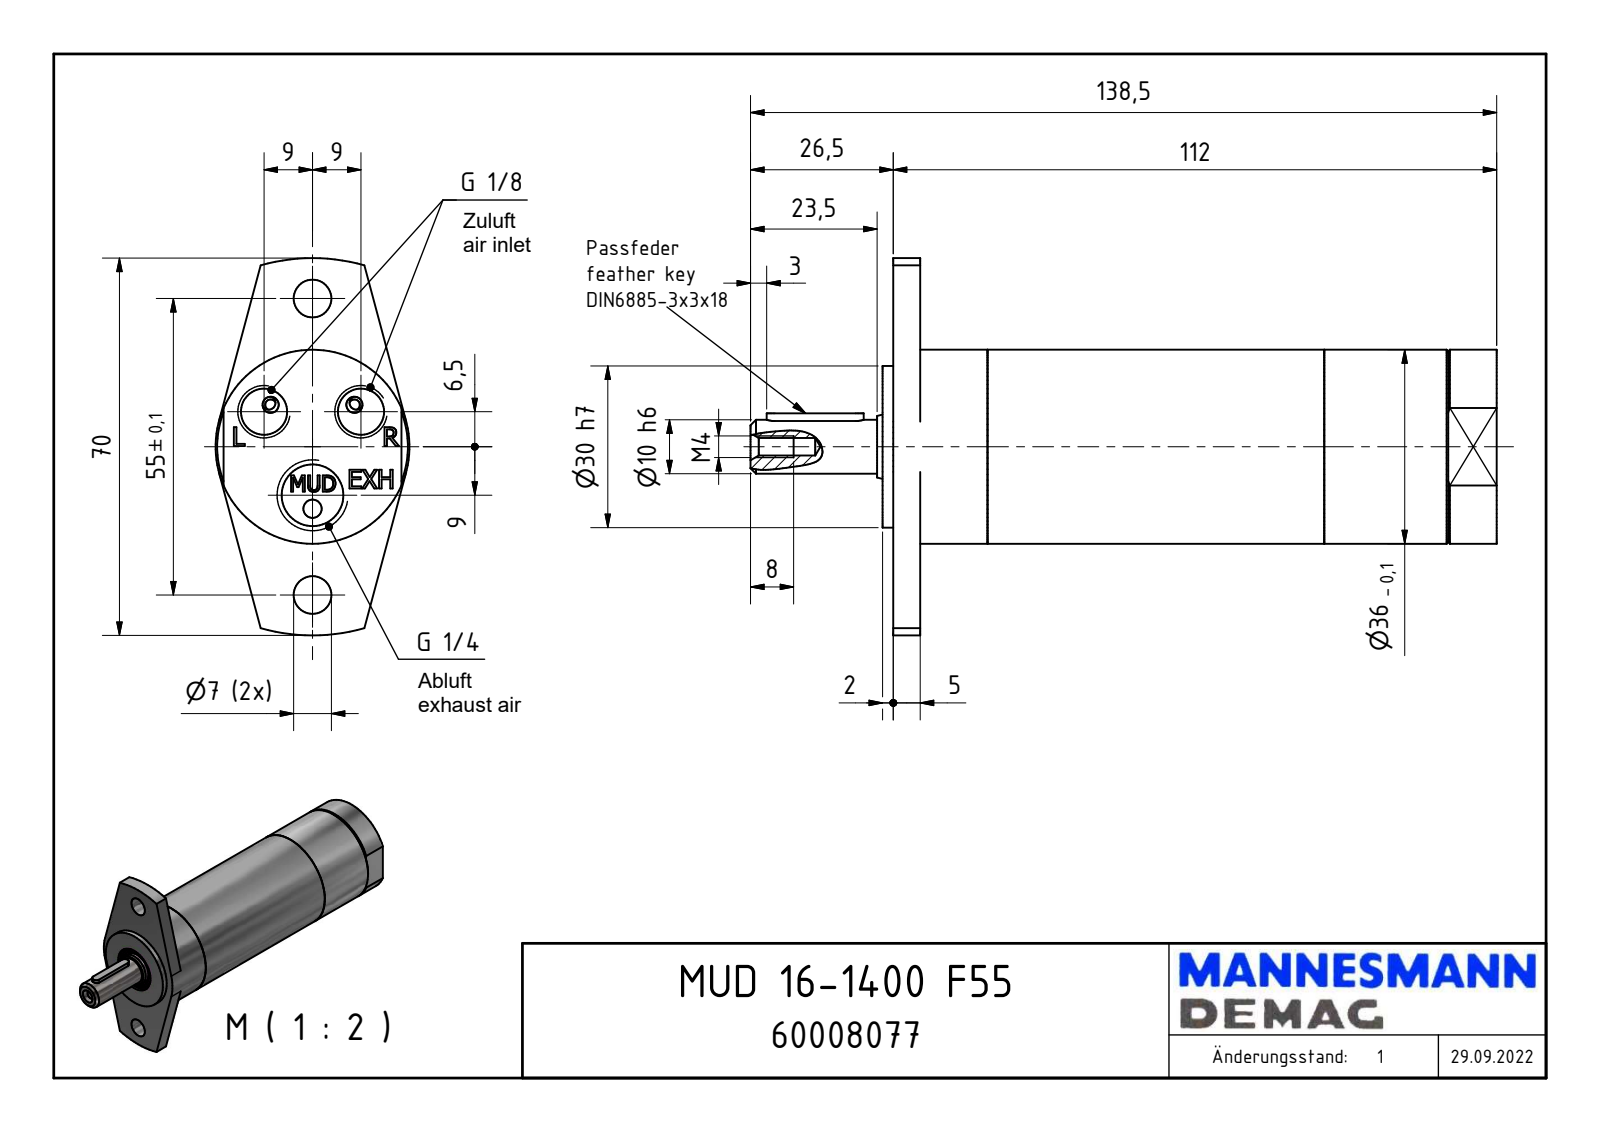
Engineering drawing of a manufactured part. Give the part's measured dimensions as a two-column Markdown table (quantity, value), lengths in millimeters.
| quantity | value |
| --- | --- |
| part name | MUD 16-1400 F55_60008077 |
| STEP written by | Autodesk Inventor 2018 (AUTOMOTIVE_DESIGN) |
| units | millimeters |
| bodies | 1 solid, 127 faces (84 planar, 22 cylindrical, 21 other) |
| overall size | 138.5 × 70 × 36 |
| volume | 118 827 mm³ |
| surface area | 19 288 mm² |
| round holes (diameter × count) | 7 × 2, 8.57 × 2, 3.24 × 1, 11.45 × 1, 15.5 × 1, 17 × 1 |
| round bosses / shafts (diameter × count) | 36 × 1, 30 × 1, 11.95 × 1, 10 × 1 |
| partial cylindrical surfaces (radius × count) | 1.5 × 2, 9.5 × 2, 35 × 1 |
| main face-to-face distances | 5, 112, 107, 2, 7, 114, 104.03, 102.03, 97.03, 9.97 |
| hole center spacings | 11.1, 17.92, 22.85, 27.5, 35.17, 0.71, 8.96, 9 |
